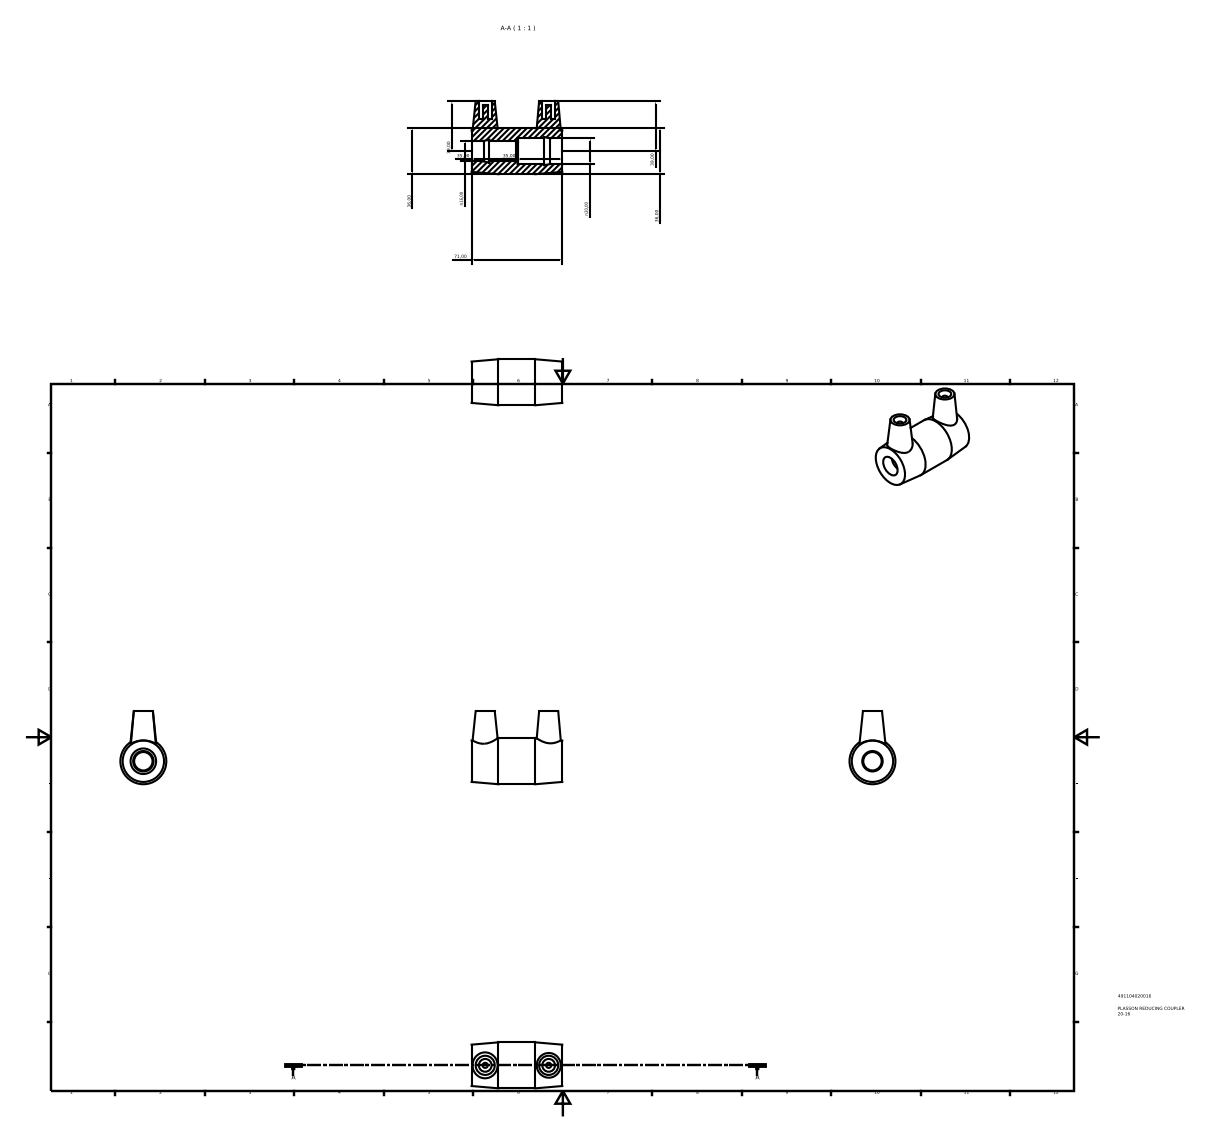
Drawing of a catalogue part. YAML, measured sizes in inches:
part_name: "491104020016"
step_written_by: "Autodesk Inventor 2015 (AUTOMOTIVE_DESIGN)"
units: inches
bodies: {solids: 1, faces: 29, planar: 12, cylindrical: 10, other: 7}
overall_size: [2.795, 2.244, 1.417]
volume: 3.557
surface_area: 25.93
round_holes:
  - {diameter: 0.394, count: 2}
  - {diameter: 0.567, count: 1}
  - {diameter: 0.63, count: 1}
  - {diameter: 0.787, count: 1}
round_bosses_or_shafts:
  - {diameter: 0.157, count: 2}
  - {diameter: 1.417, count: 1}
face_to_face_distances: [2.795, 0.551, 2.244, 1.693, 1.417, 0.865, 0.828, 1.379, 1.378, 0.827]
hole_center_spacings: [1.957]
